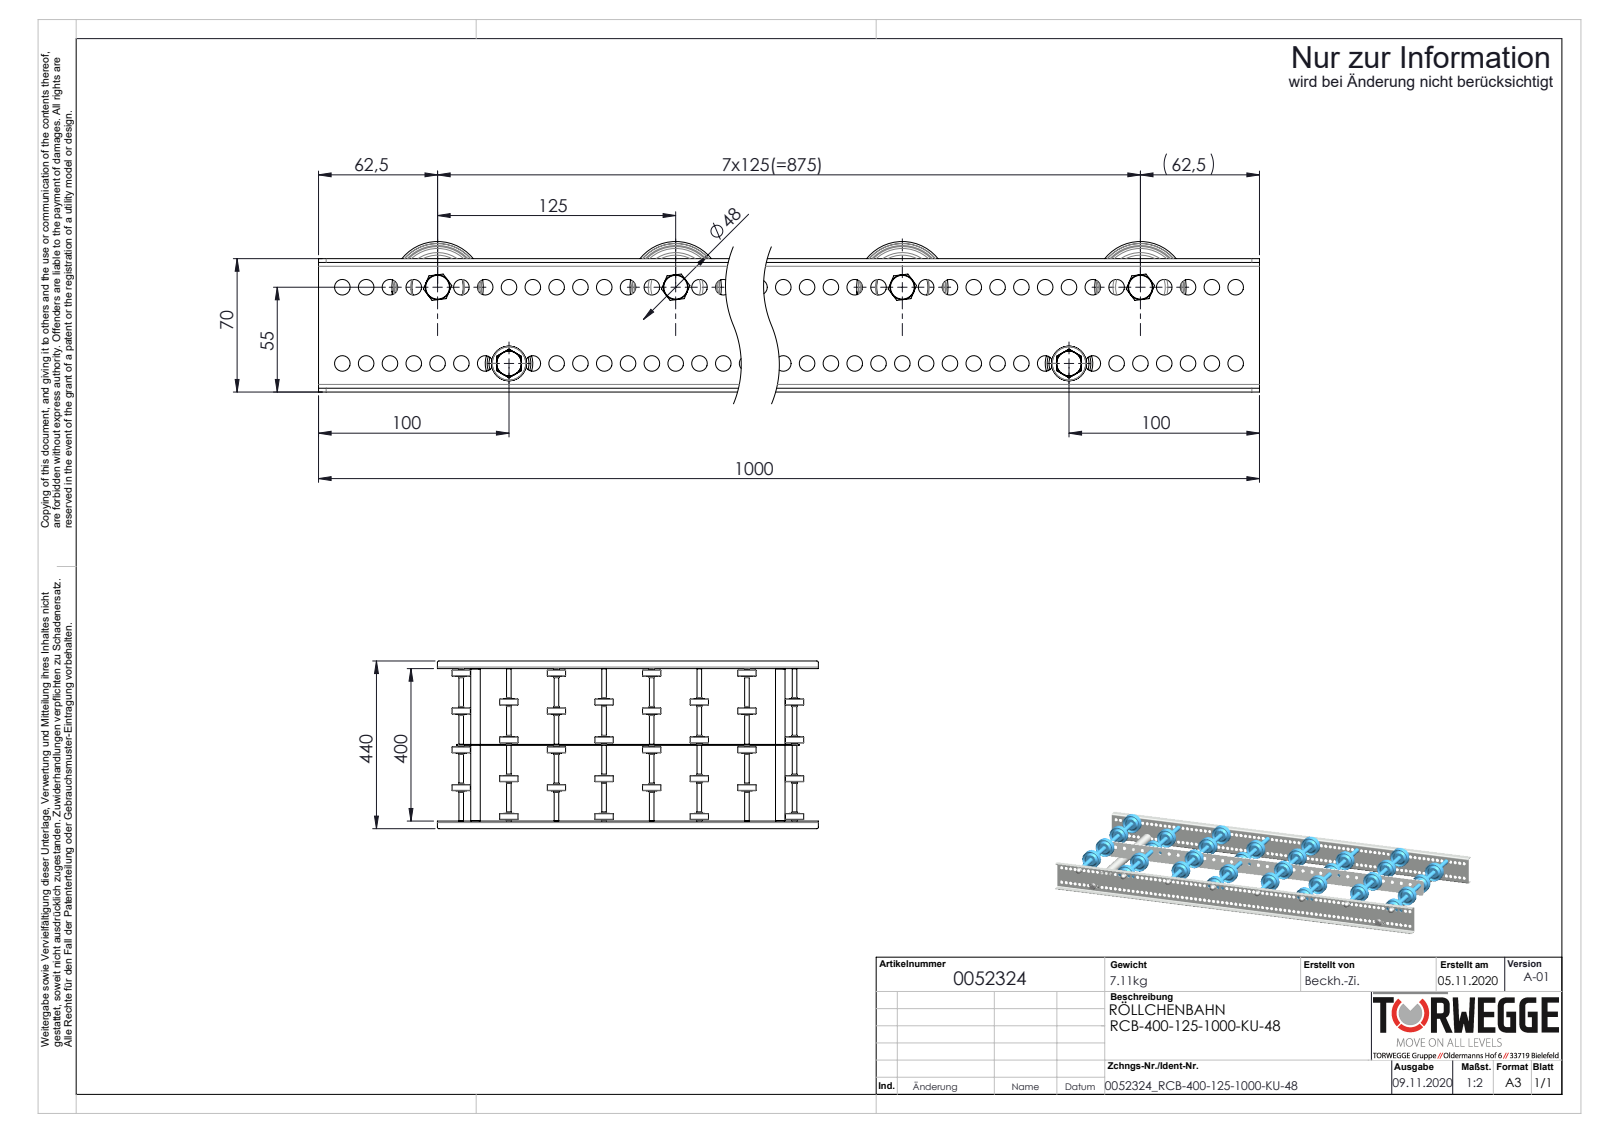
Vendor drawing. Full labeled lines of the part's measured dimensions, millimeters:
Part name (STEP PRODUCT): Hutmutter_DIN_1587_M8; 0052324; S106837_Gewindestange-M8-KFG_L420; S100994_Sperrzahnschraube_M08x16-8.8-A2K (+6 more)
STEP written by: SolidWorks 2020 (AUTOMOTIVE_DESIGN)
Units: millimetres
Bodies: 101 solids, 3906 faces (686 planar, 1548 cylindrical, 1672 other)
Overall size (bounding box): 1000 × 440 × 79
Volume: 1 503 000 mm³ · Surface area: 1 185 000 mm²
Round holes (diameter × count): ⌀8.2 ×158, ⌀8.5 ×36, ⌀6.65 ×8, ⌀9.65 ×8, ⌀13.7 ×8, ⌀6.8 ×2, ⌀21 ×2
Round bosses / shafts (diameter × count): ⌀8 ×10, ⌀48 ×8, ⌀27 ×8, ⌀12.7 ×8, ⌀12.5 ×8, ⌀12 ×8, ⌀25 ×2
Partial cylindrical surfaces — rounded edges, fillets, slot ends (radius × count): R4 ×8, R2 ×4, R5 ×4
Main face-to-face distances: 2, 402, 68, 404, 400, 201.1, 198.6, 200.9, 198.9, 203.1
Hole centre spacings: 12.5, 25, 37.5, 50, 62.5, 75, 87.5, 100
